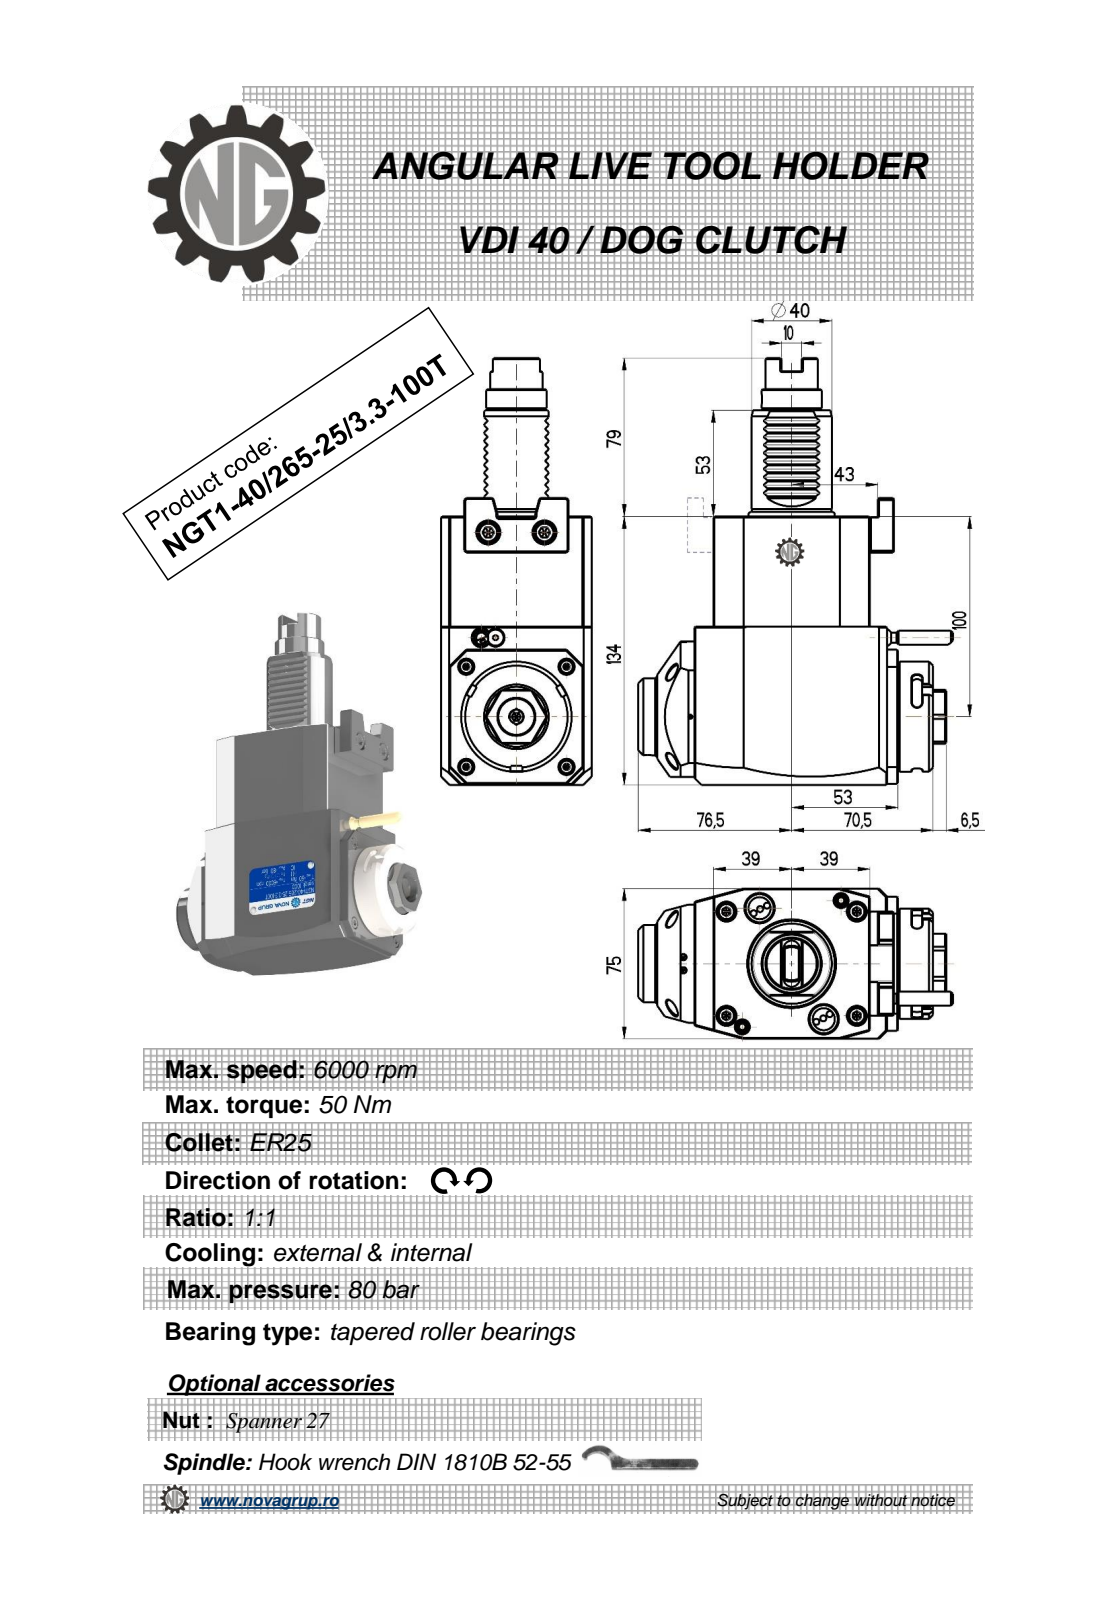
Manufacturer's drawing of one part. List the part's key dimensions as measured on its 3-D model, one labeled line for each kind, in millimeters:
Part name (STEP PRODUCT): NGT1_40_265_25_3_3_100T
STEP written by: PRO/ENGINEER BY PARAMETRIC TECHNOLOGY CORPORATION, 2010280 (CONFIG_CONTROL_DESIGN)
Units: millimetres
Bodies: 1 solid, 387 faces (239 planar, 80 cylindrical, 68 other)
Overall size (bounding box): 213 × 156.83 × 75
Volume: 1 084 000 mm³ · Surface area: 78 124 mm²
Round holes (diameter × count): ⌀2.5 ×1, ⌀3 ×1, ⌀4.2 ×1, ⌀18 ×1
Round bosses / shafts (diameter × count): ⌀55 ×1, ⌀48 ×1, ⌀40 ×1, ⌀38.5 ×1, ⌀30 ×1, ⌀26 ×1, ⌀8 ×1, ⌀7 ×1
Partial cylindrical surfaces — rounded edges, fillets, slot ends (radius × count): R0.3 ×20, R0.26 ×6, R2.5 ×6, R0.5 ×2, R1 ×2, R180 ×2, R12.5 ×1, R15 ×1
Main face-to-face distances: 75, 134, 78, 14, 92, 17.5, 31.5, 84.88, 109.5, 4
Hole centre spacings: 43.2, 120.28, 158.5
